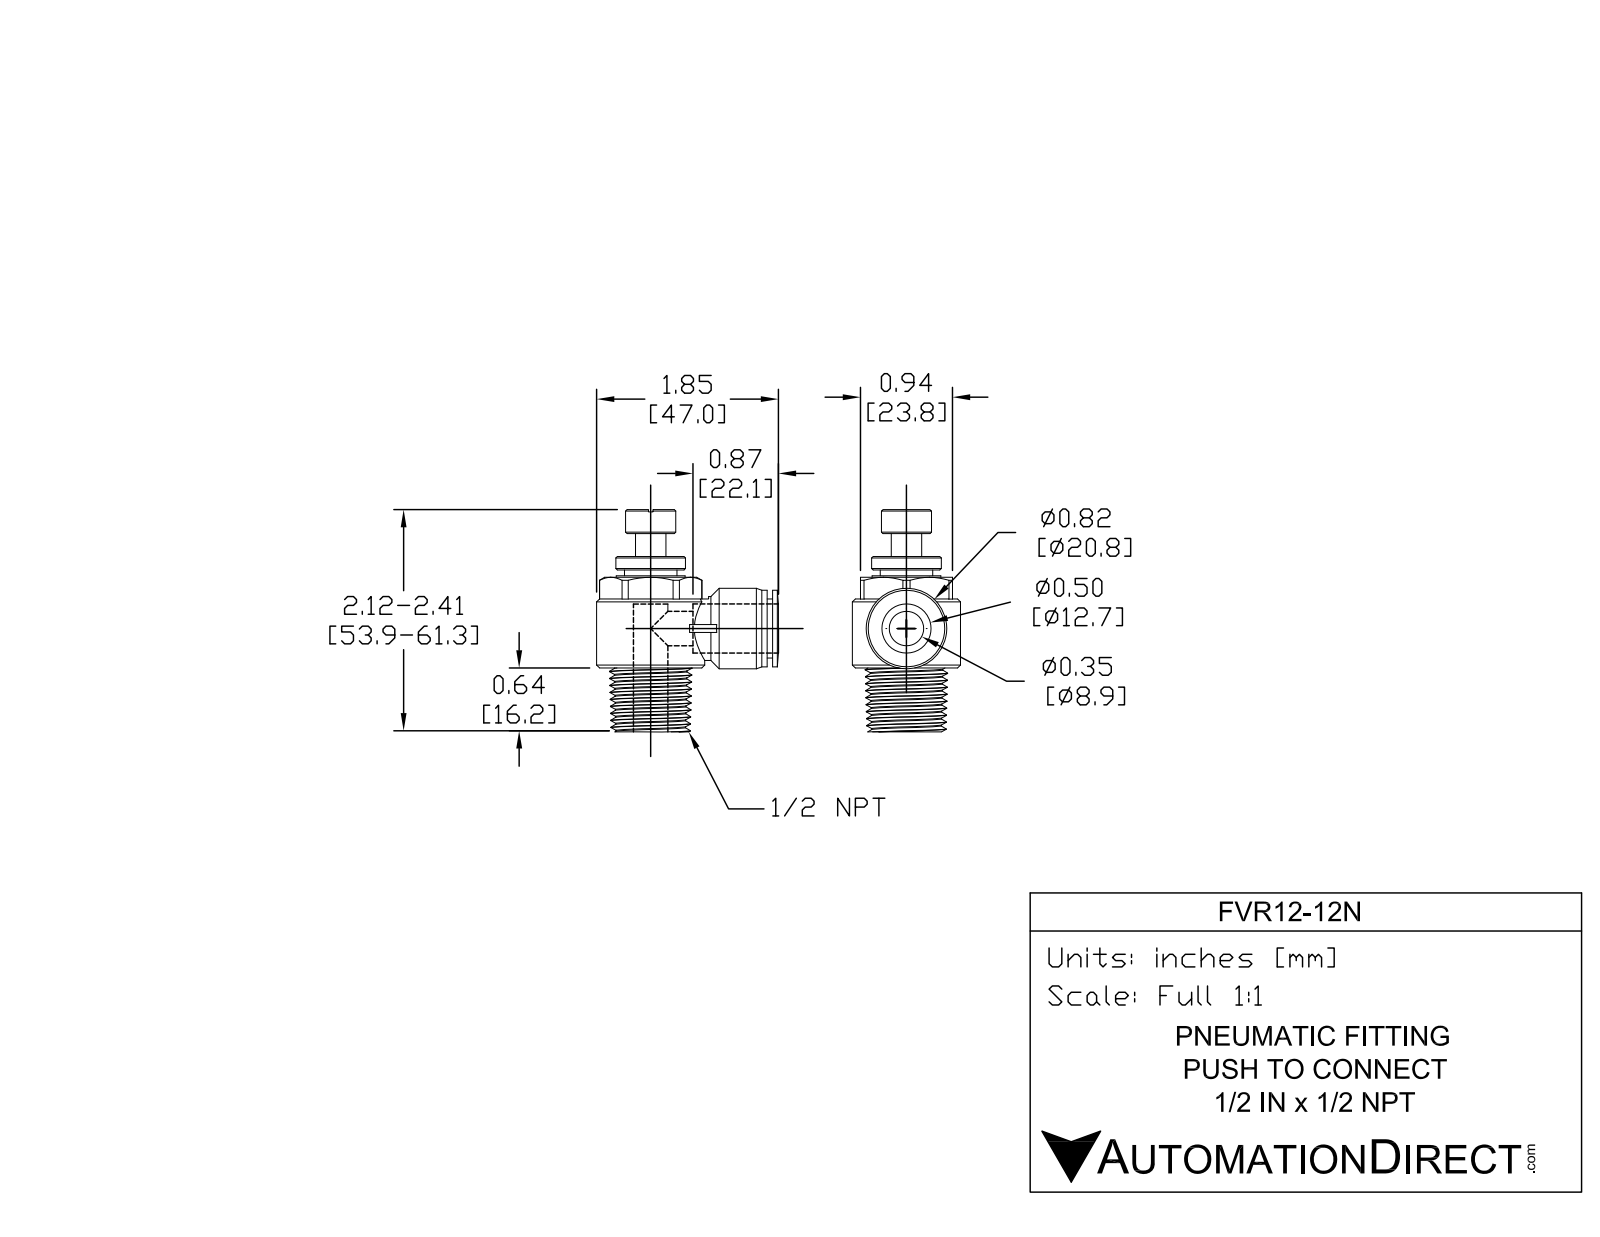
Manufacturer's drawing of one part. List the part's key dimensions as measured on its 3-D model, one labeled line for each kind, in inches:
Part name (STEP PRODUCT): FVR12-12N
STEP written by: SolidWorks 2015 (AUTOMOTIVE_DESIGN)
Units: inches
Bodies: 1 solid, 579 faces (259 planar, 150 cylindrical, 170 other)
Overall size (bounding box): 2.413 × 1.986 × 1.102
Volume: 1.481 in³ · Surface area: 14.31 in²
Round holes (diameter × count): ⌀0.315 ×2, ⌀0.51 ×1
Round bosses / shafts (diameter × count): ⌀1.102 ×1, ⌀0.945 ×1, ⌀0.864 ×1, ⌀0.819 ×1, ⌀0.787 ×1, ⌀0.783 ×1, ⌀0.713 ×1, ⌀0.65 ×1
Partial cylindrical surfaces — rounded edges, fillets, slot ends (radius × count): R0.256 ×1, R0.354 ×1, R0.512 ×1
Main face-to-face distances: 1.622, 0.697, 0.925, 1.831, 1.134, 0.209, 0.945, 0.051, 1.693, 0.996
